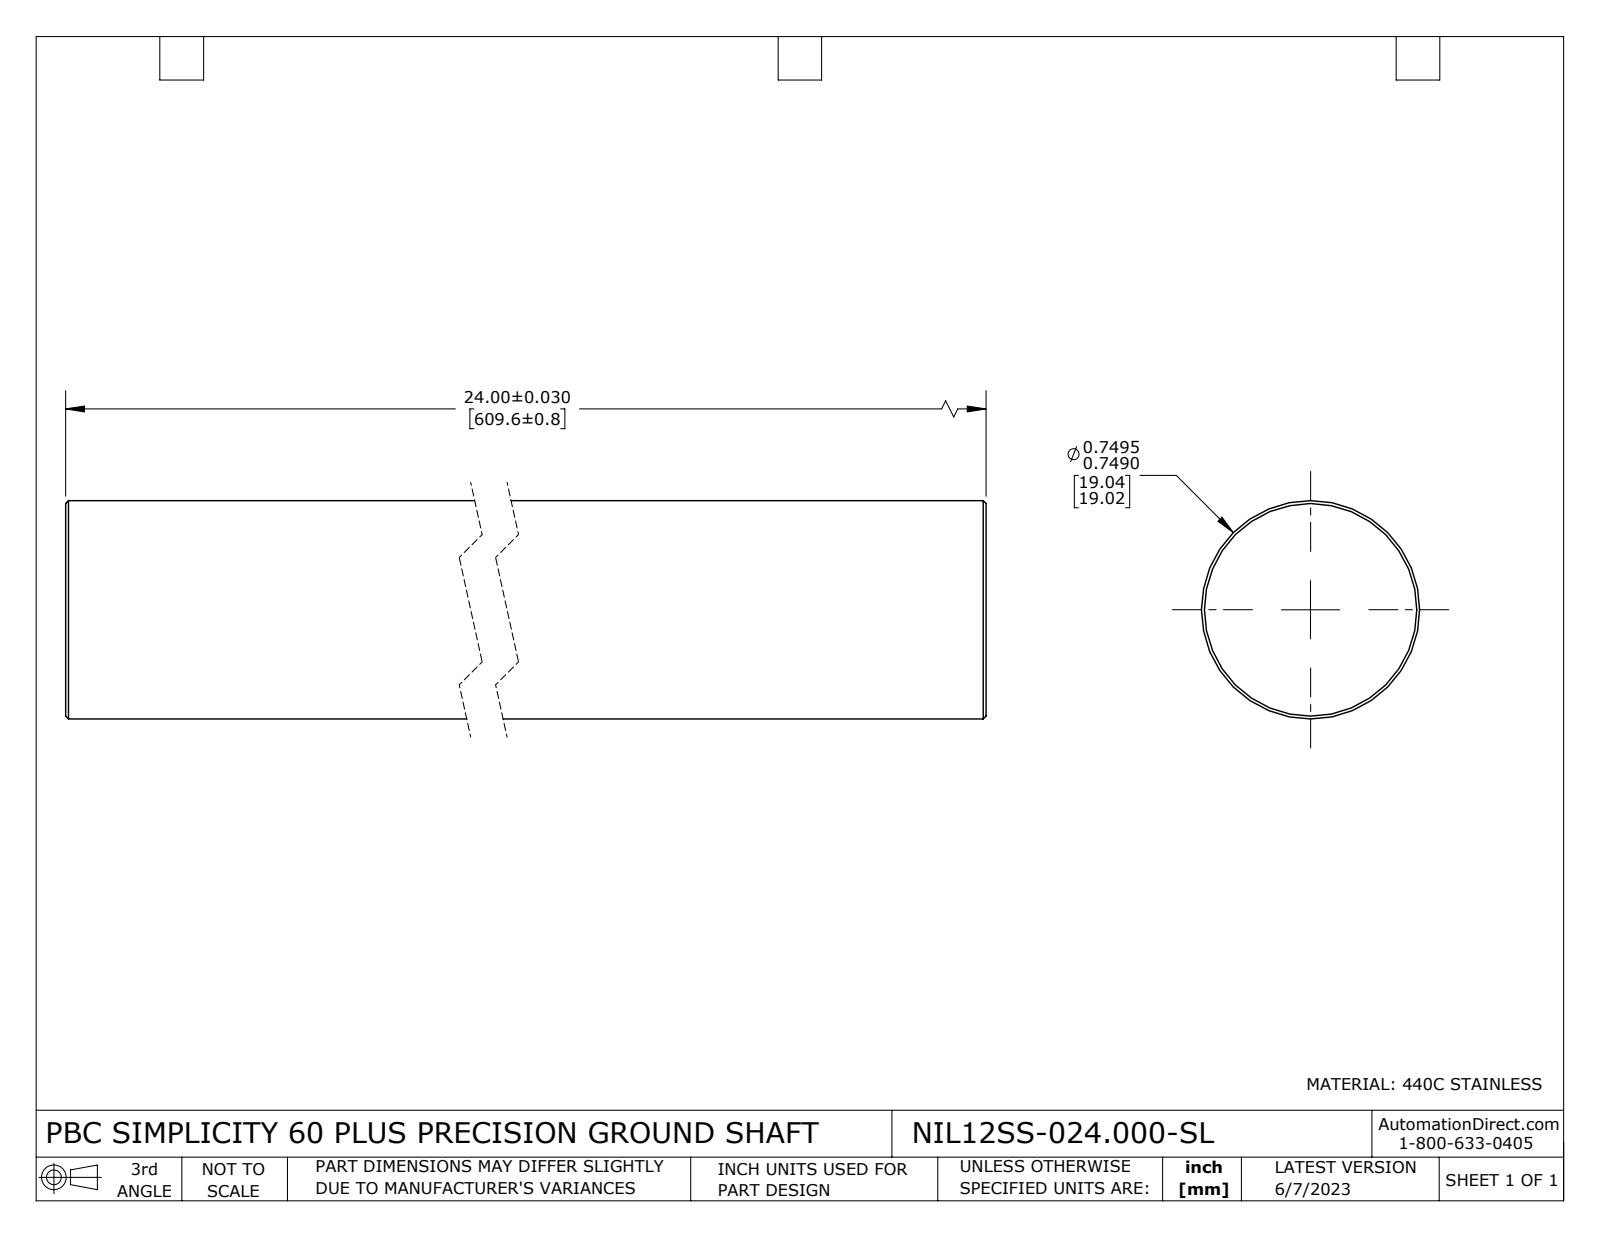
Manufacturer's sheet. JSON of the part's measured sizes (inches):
{"part_name": "NIL12SS-024.000-SL", "step_written_by": "SolidWorks 2021 (CONFIG_CONTROL_DESIGN)", "units": "inches", "bodies": {"solids": 1, "faces": 8, "planar": 2, "cylindrical": 2, "other": 4}, "overall_size": [24, 0.75, 0.75], "volume_in3": 10.6, "surface_area_in2": 57.4, "round_bosses_or_shafts": [[0.75, 1]], "face_to_face_distances": [24]}
